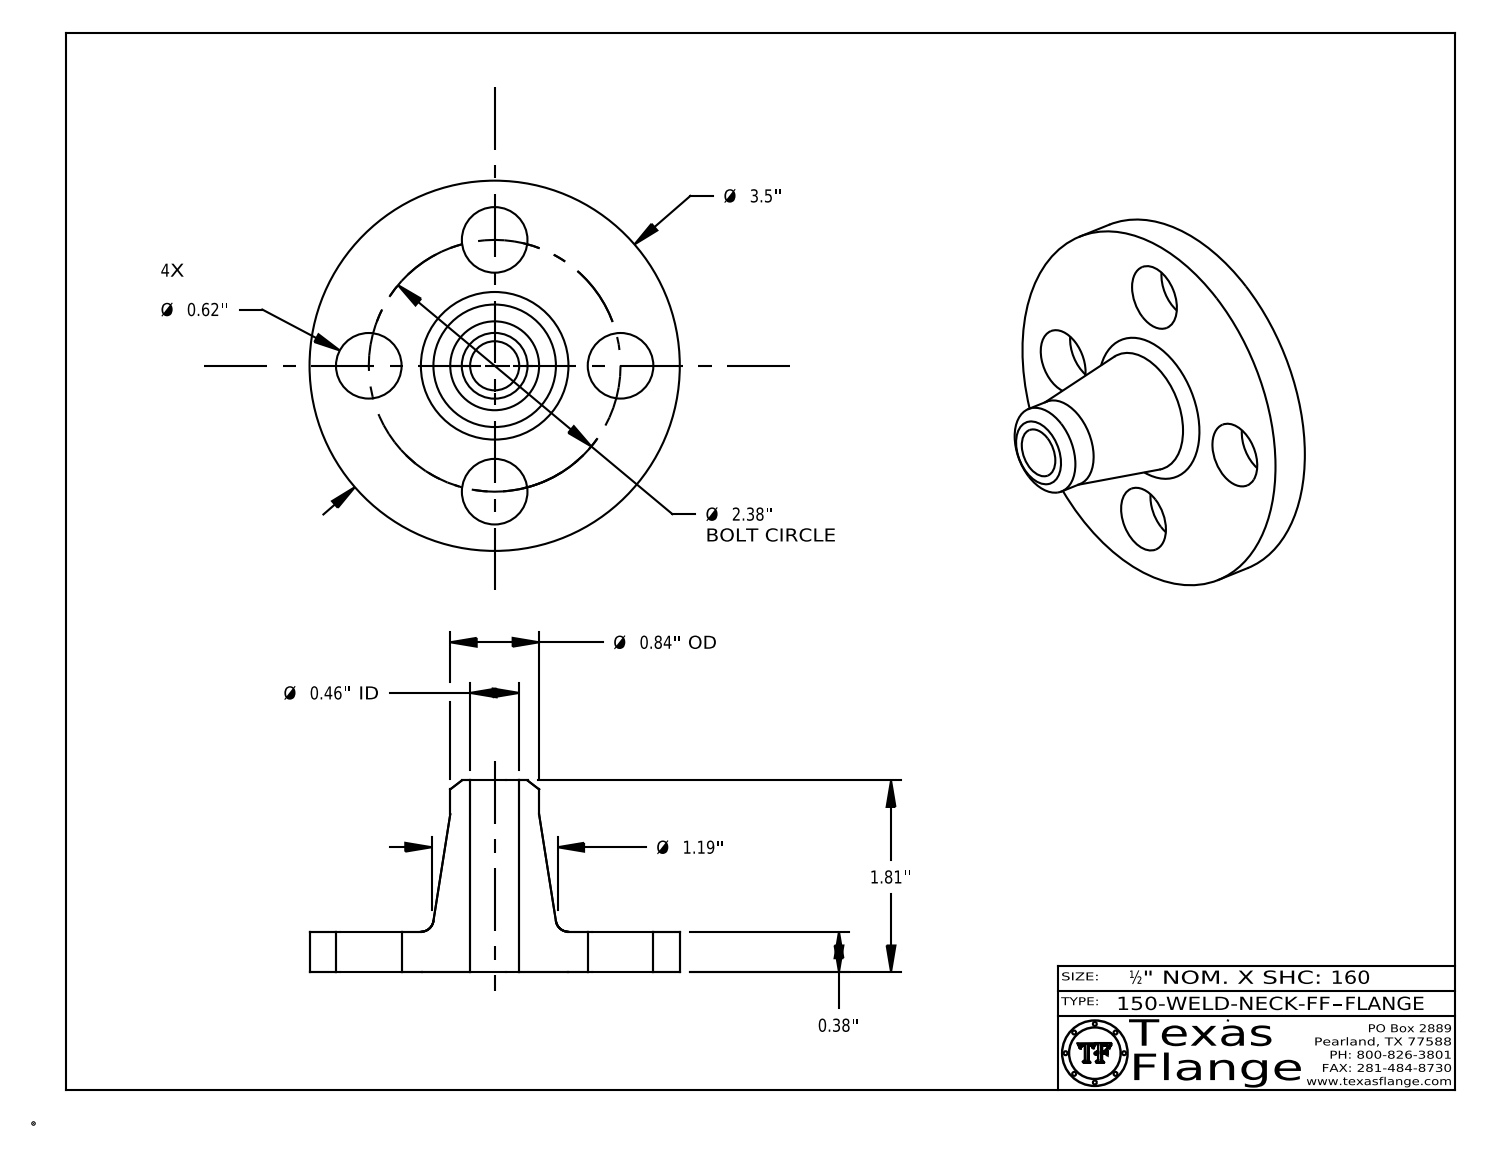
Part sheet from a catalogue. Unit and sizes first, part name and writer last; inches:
Units: inches
Overall size (bounding box): 3.5 × 3.5 × 1.81
Round holes (diameter × count): ⌀0.62 ×4, ⌀0.464 ×1, ⌀0.495 ×1
Round bosses / shafts (diameter × count): ⌀0.03 ×8, ⌀3.5 ×1, ⌀0.84 ×1, ⌀0.39 ×1
Main face-to-face distances: 0.38, 1.81, 1.43, 0.365, 0.015, 1.445, 0.148, 0.145, 0.027, 0.096
Hole centre spacings: 1.19, 1.683, 0.911, 2.199, 2.38, 1.19
Volume: 3.971 in³ · Surface area: 29.95 in²
Bodies: 1 solid, 409 faces (369 planar, 34 cylindrical, 6 other)
Part name (STEP PRODUCT): 150-WELD-NECK-FF
STEP written by: CATIA V5 STEP AP214 (AUTOMOTIVE_DESIGN)
